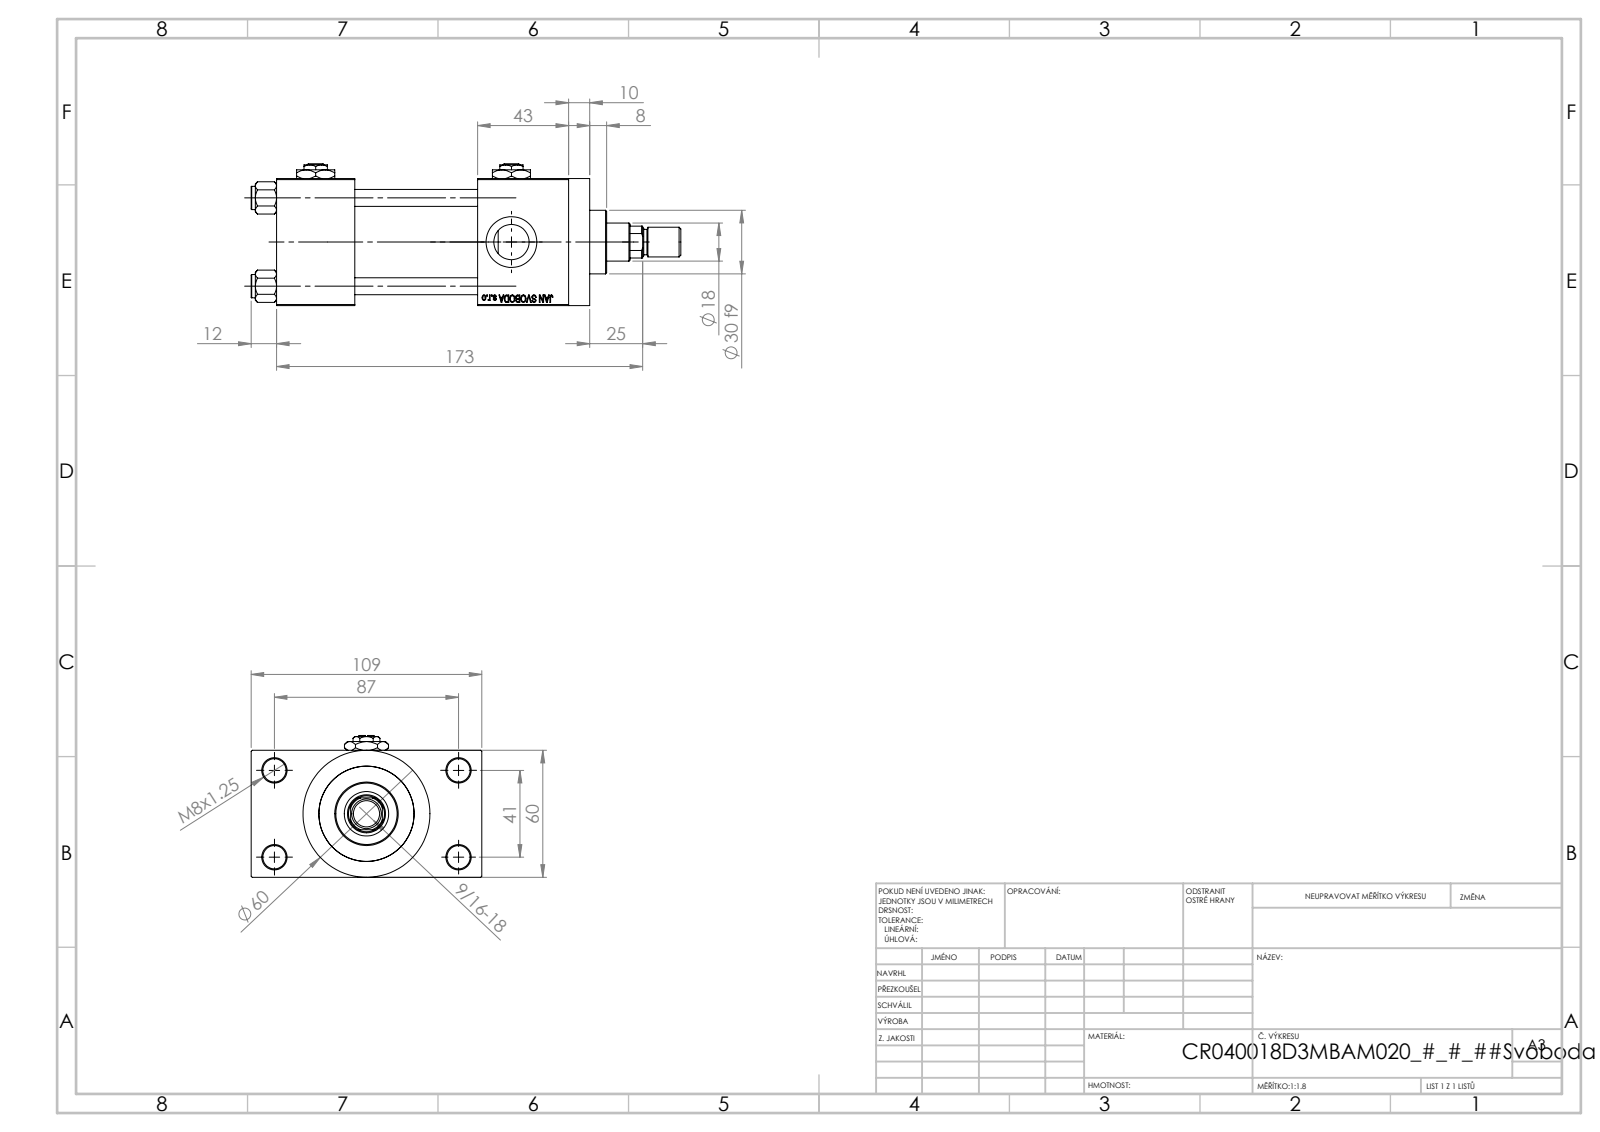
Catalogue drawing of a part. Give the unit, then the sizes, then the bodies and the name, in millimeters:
Units: millimetres
Overall size (bounding box): 203 × 109 × 67
Round holes (diameter × count): ⌀8 ×4, ⌀11 ×4, ⌀16.66 ×4, ⌀24 ×4, ⌀7 ×3, ⌀8.5 ×1, ⌀18 ×1, ⌀21 ×1, ⌀31 ×1, ⌀40 ×1, ⌀45 ×1
Round bosses / shafts (diameter × count): ⌀11 ×4, ⌀60 ×1, ⌀46 ×1, ⌀30 ×1, ⌀14 ×1, ⌀12 ×1
Partial cylindrical surfaces — rounded edges, fillets, slot ends (radius × count): R8.5 ×1
Main face-to-face distances: 60, 58, 84.5, 24.5, 37, 95, 43, 138, 101, 53
Hole centre spacings: 22.65, 29.49, 41.7, 47.15, 48.09, 64.35, 76.49, 41
Volume: 513 315 mm³ · Surface area: 126 233 mm²
Bodies: 14 solids, 1219 faces (550 planar, 103 cylindrical, 566 other)
Part name (STEP PRODUCT): V215CR_VCP_D; V215CR_D_TYCINKA; Zatka_pro_OIL_PORT; ROD_END_AH (+3 more)
STEP written by: SolidWorks 2019 (CONFIG_CONTROL_DESIGN)
